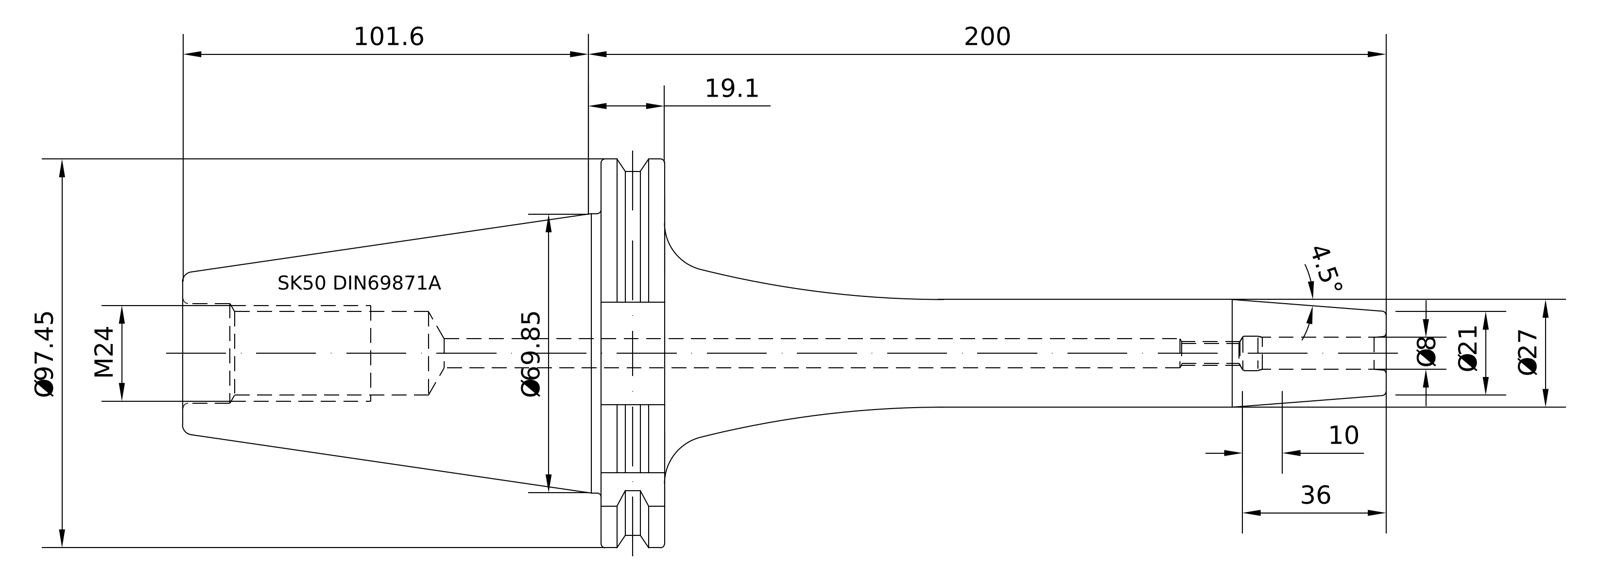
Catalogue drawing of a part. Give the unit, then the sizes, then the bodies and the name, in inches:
Units: inches
Overall size (bounding box): 11.874 × 3.837 × 3.701
Round holes (diameter × count): ⌀0.315 ×1, ⌀0.817 ×1, ⌀0.985 ×1, ⌀1.012 ×1
Round bosses / shafts (diameter × count): ⌀3.583 ×1, ⌀2.722 ×1, ⌀1.063 ×1, ⌀0.945 ×1
Partial cylindrical surfaces — rounded edges, fillets, slot ends (radius × count): R0.069 ×1, R1.919 ×1
Main face-to-face distances: 0.624, 2.866, 4.126, 4.75, 1.016, 11.874, 7.748, 7.124, 1.89, 2.236
Volume: 28.26 in³ · Surface area: 90.44 in²
Bodies: 1 solid, 95 faces (21 planar, 24 cylindrical, 50 other)
Part name (STEP PRODUCT): 50-446-08
STEP written by: PRO/ENGINEER BY PARAMETRIC TECHNOLOGY CORPORATION, 2010430 (CONFIG_CONTROL_DESIGN)
